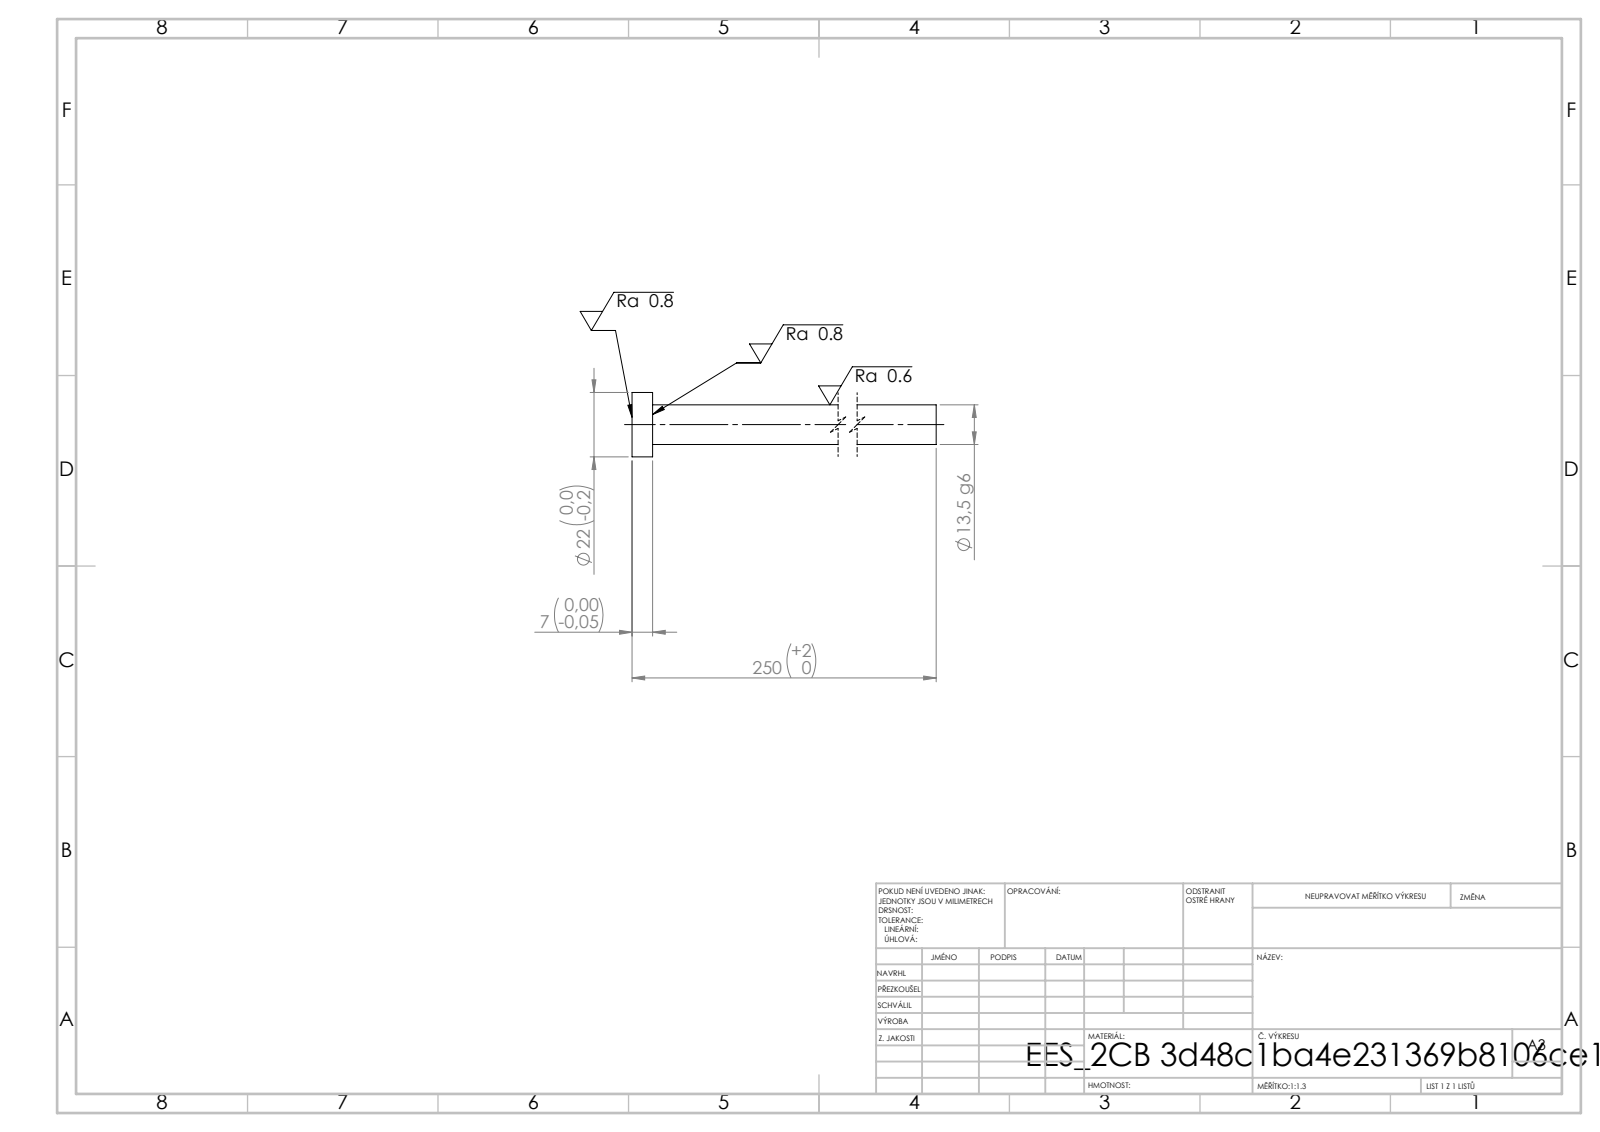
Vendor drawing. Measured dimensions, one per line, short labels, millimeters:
written by: SolidWorks 2019 (CONFIG_CONTROL_DESIGN)
unit: mm
bodies: 1 solid, 7 faces (3 planar, 4 cylindrical, 0 other)
size: 250 × 22 × 22
volume: 37 444 mm³; area: 11 550 mm²
bosses: 1× ⌀22, 1× ⌀13.5
face distances: 7, 250, 243
